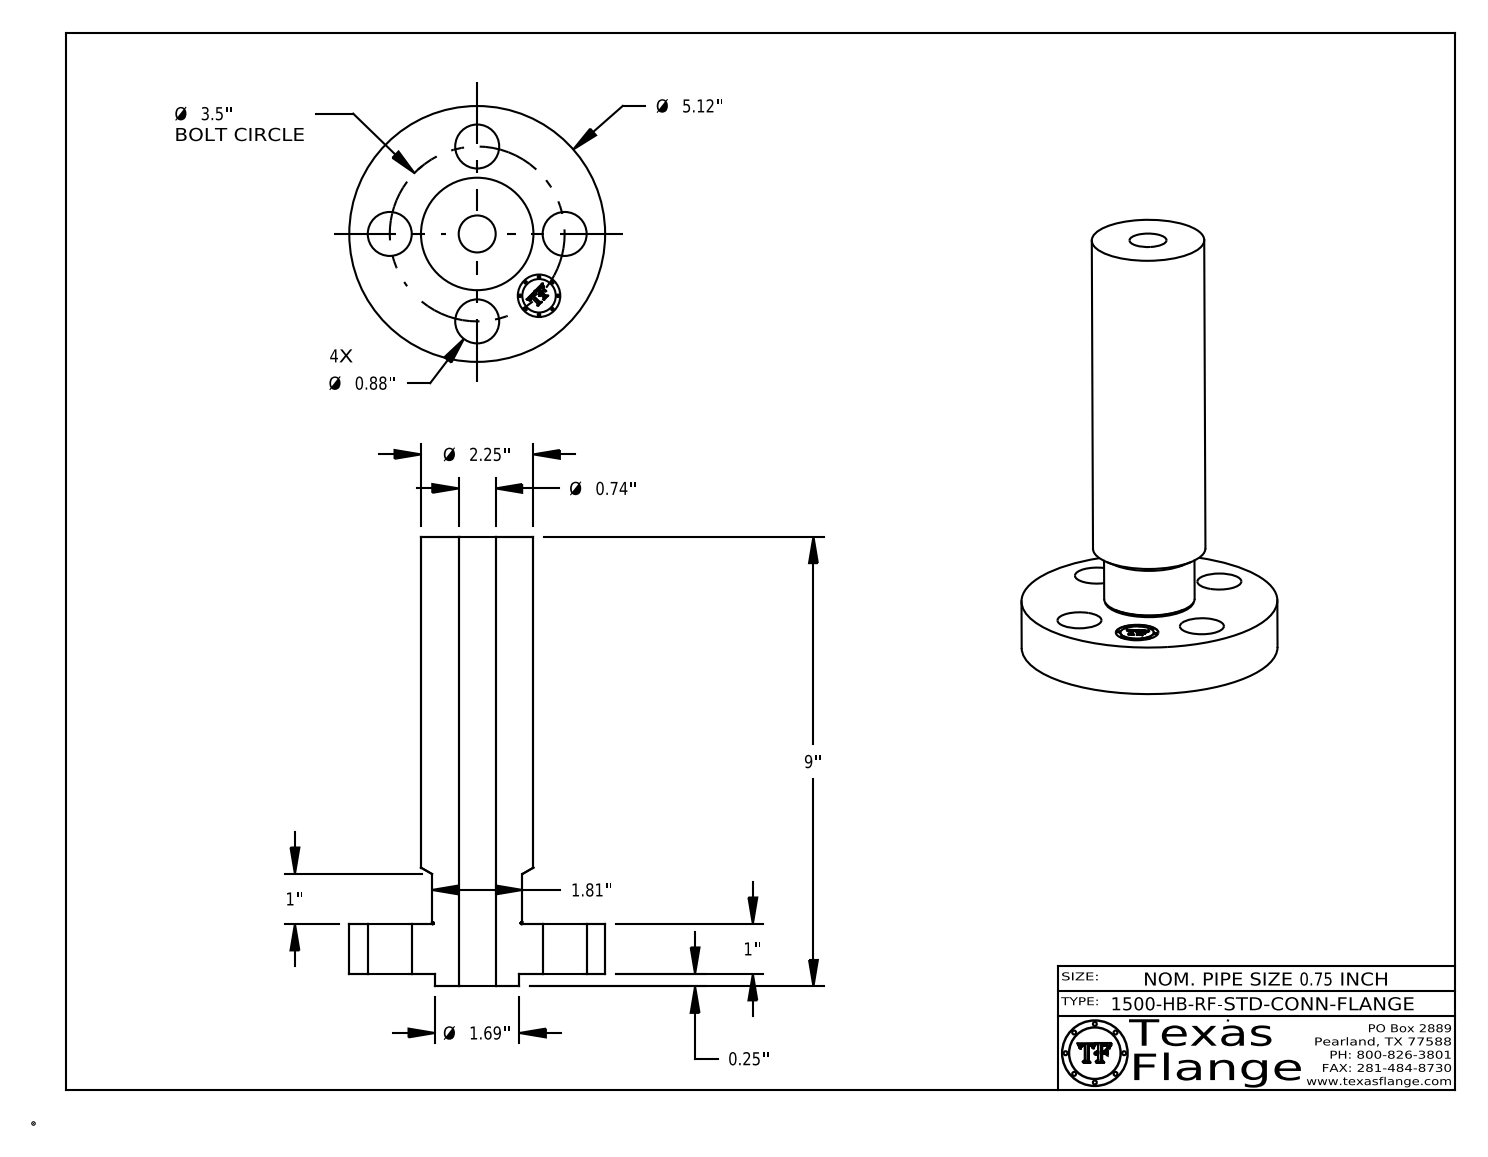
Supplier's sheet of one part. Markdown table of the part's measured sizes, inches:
| quantity | value |
| --- | --- |
| part name | 0.75-1500-HB-RF-STD-CONN-FLANGE |
| STEP written by | CATIA V5 STEP AP214 (AUTOMOTIVE_DESIGN) |
| units | inches |
| bodies | 1 solid, 413 faces (369 planar, 38 cylindrical, 6 other) |
| overall size | 9 × 5.12 × 5.12 |
| volume | 44.16 in³ |
| surface area | 140.6 in² |
| round holes (diameter × count) | 0.88 × 4, 0.74 × 1, 0.85 × 1 |
| round bosses / shafts (diameter × count) | 0.051 × 8, 5.12 × 1, 2.25 × 1, 1.81 × 1, 1.69 × 1, 0.67 × 1 |
| main face-to-face distances | 1, 8.75, 7.75, 0.25, 1.25, 9, 1.245, 0.995, 7.755, 0.016 |
| hole center spacings | 1.75, 2.475, 1.339, 3.233, 3.5 |
